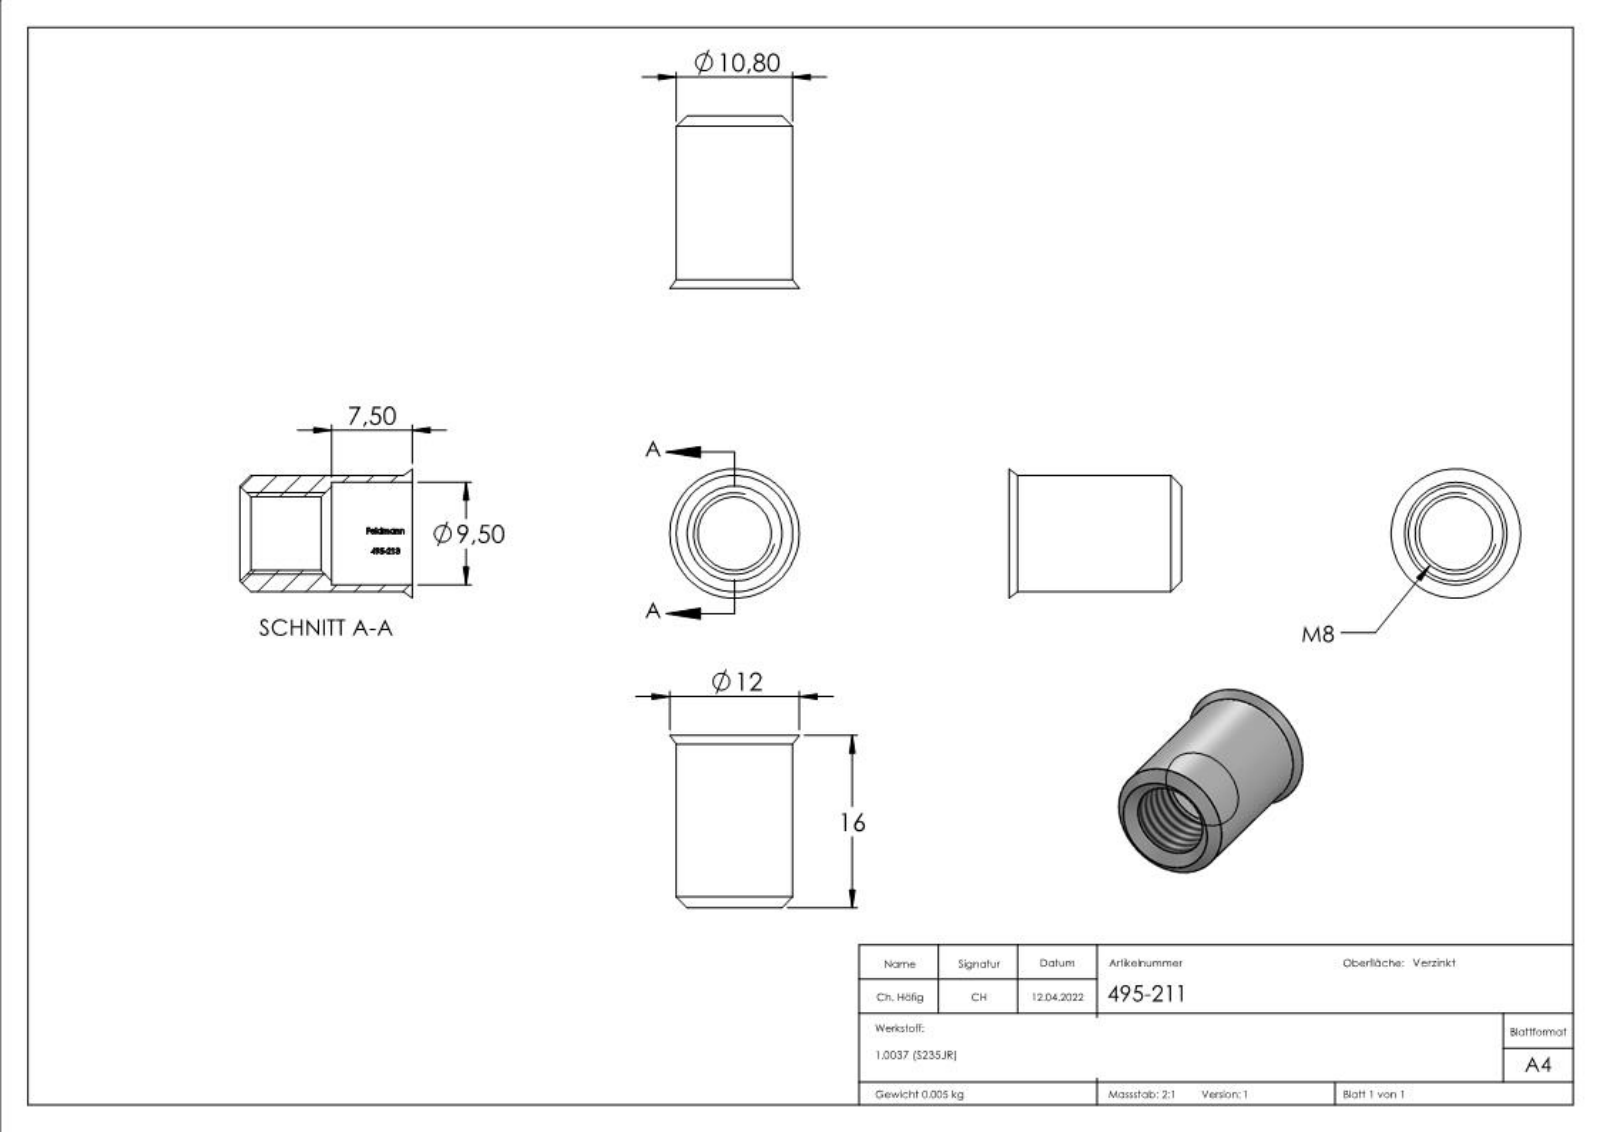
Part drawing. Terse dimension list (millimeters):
name: 495-211
written by: SolidWorks 2018 (CONFIG_CONTROL_DESIGN)
unit: mm
bodies: 1 solid, 210 faces (100 planar, 29 cylindrical, 81 other)
size: 16 × 12 × 12
volume: 594 mm³; area: 1 049 mm²
holes: 1× ⌀6.8, 1× ⌀9.5
bosses: 1× ⌀10.8
rounds: 1× R4.85
face distances: 7.5, 1.83, 0.66, 1.35, 1.88, 1.19, 1.67, 1.74, 1.62, 1.79
